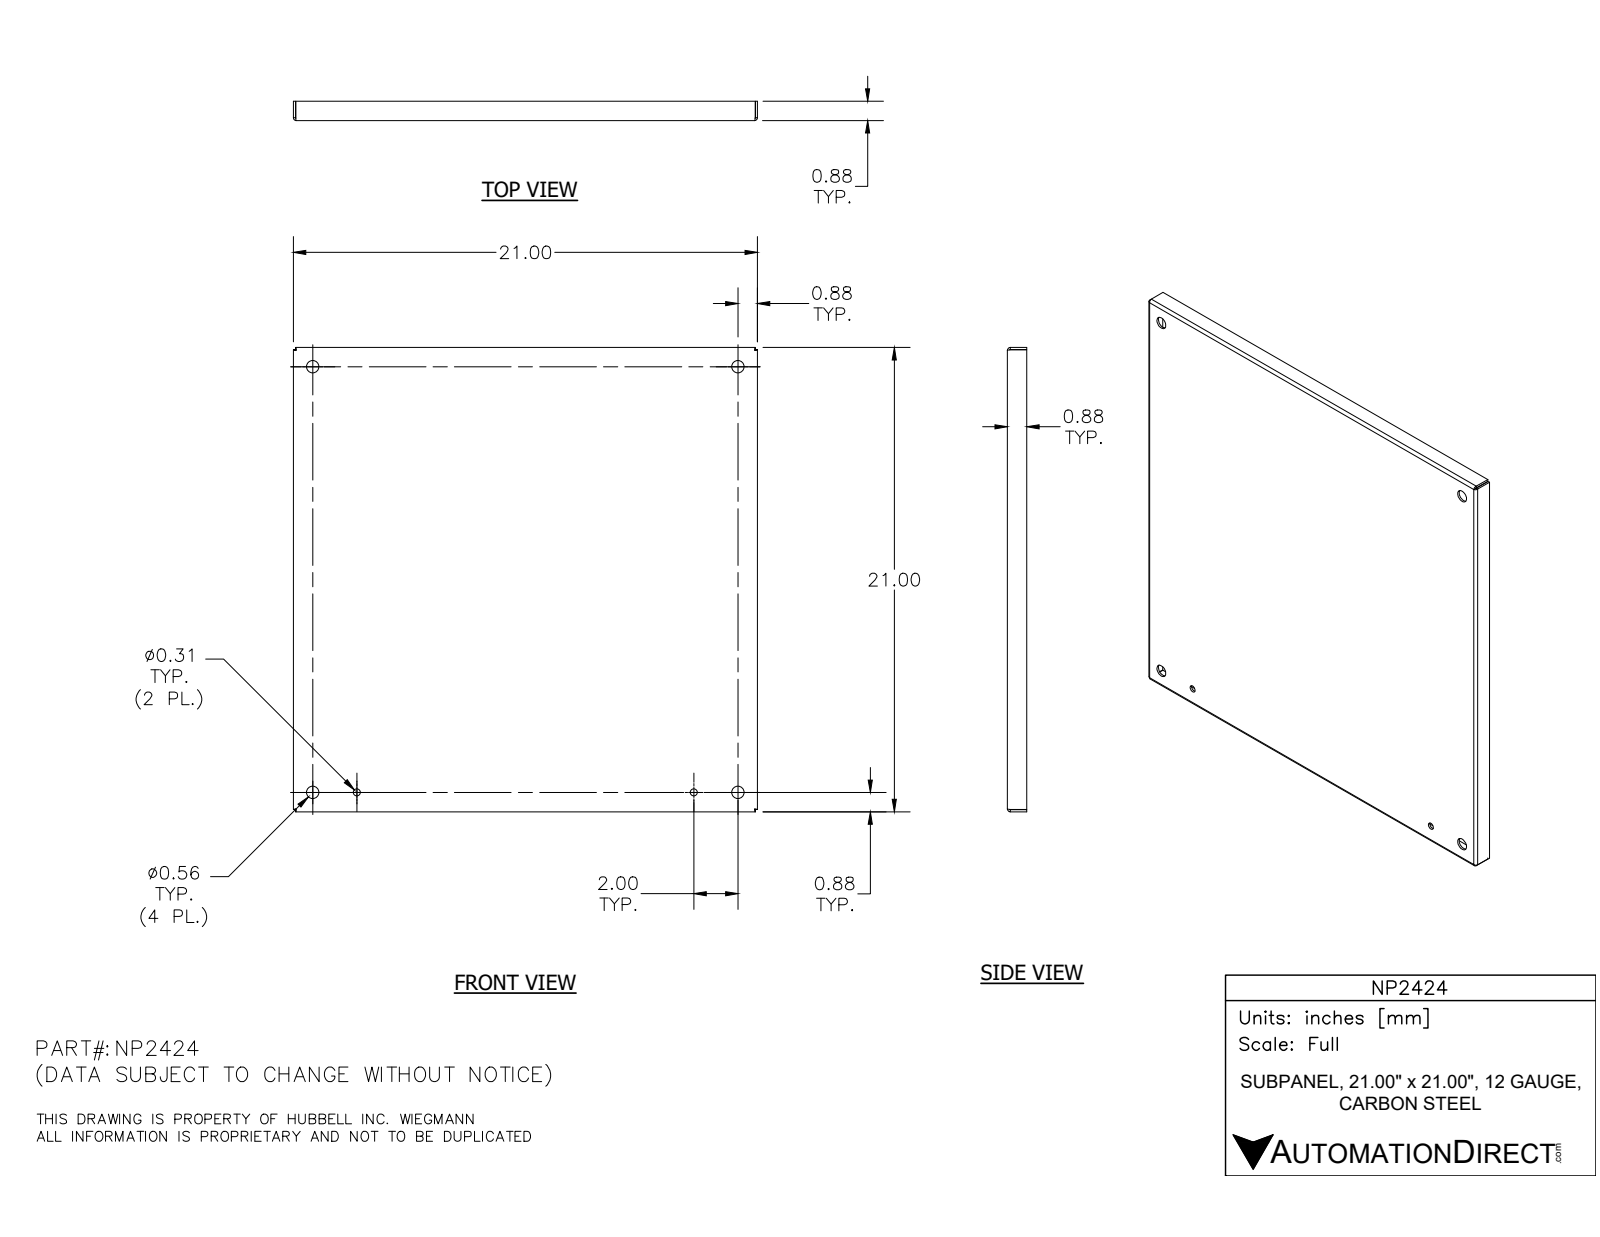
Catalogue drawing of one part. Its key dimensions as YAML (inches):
part_name: "NP2424"
step_written_by: "Autodesk Inventor 2012 (AUTOMOTIVE_DESIGN)"
units: inches
bodies: {solids: 1, faces: 44, planar: 22, cylindrical: 14, other: 8}
overall_size: [21, 21, 0.875]
volume: 47.06
surface_area: 1013
round_holes:
  - {diameter: 0.563, count: 4}
  - {diameter: 0.312, count: 2}
partial_cylinders:
  - {radius: 0.031, count: 4}
  - {radius: 0.125, count: 4}
face_to_face_distances: [0.094, 20.906, 21, 20.813, 0.781, 0.875, 0.105, 20.895, 20.802, 20.791]
hole_center_spacings: [19.25, 19.354, 27.224, 2, 2, 15.25, 17.25, 17.25]
